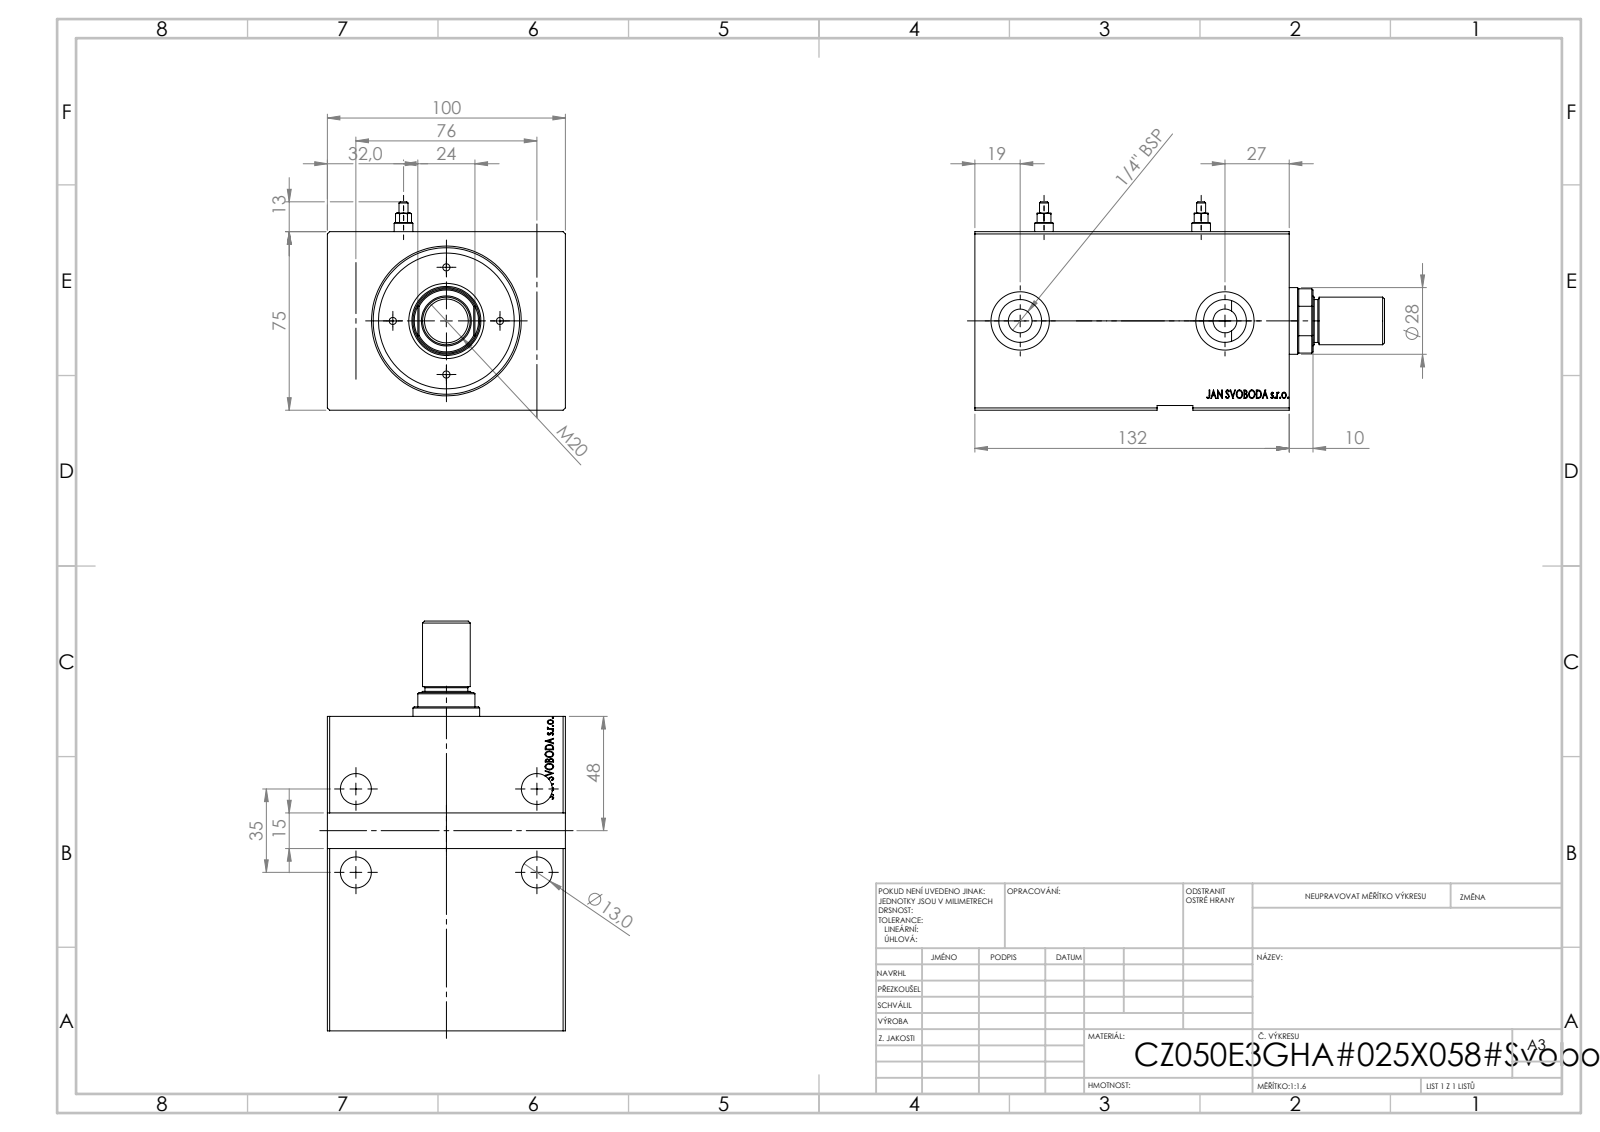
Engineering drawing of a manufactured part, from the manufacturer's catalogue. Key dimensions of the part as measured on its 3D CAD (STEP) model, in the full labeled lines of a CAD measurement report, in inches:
STEP written by: SolidWorks 2019 (CONFIG_CONTROL_DESIGN)
Units: inches
Bodies: 1 solid, 776 faces (375 planar, 31 cylindrical, 370 other)
Overall size (bounding box): 5.197 × 3.937 × 2.953
Volume: 43.06 in³ · Surface area: 142.7 in²
Round holes (diameter × count): ⌀0.512 ×4, ⌀0.315 ×2, ⌀0.394 ×2, ⌀0.709 ×2, ⌀0.965 ×2, ⌀1.417 ×1, ⌀1.969 ×1, ⌀2.421 ×1
Main face-to-face distances: 2.953, 3.937, 5.197, 4.496, 0.701, 0.079, 2.874, 5.189, 0.693, 0.394
Hole centre spacings: 1.378, 2.992, 3.294, 0.828, 1.371, 1.673, 2.22, 2.474
